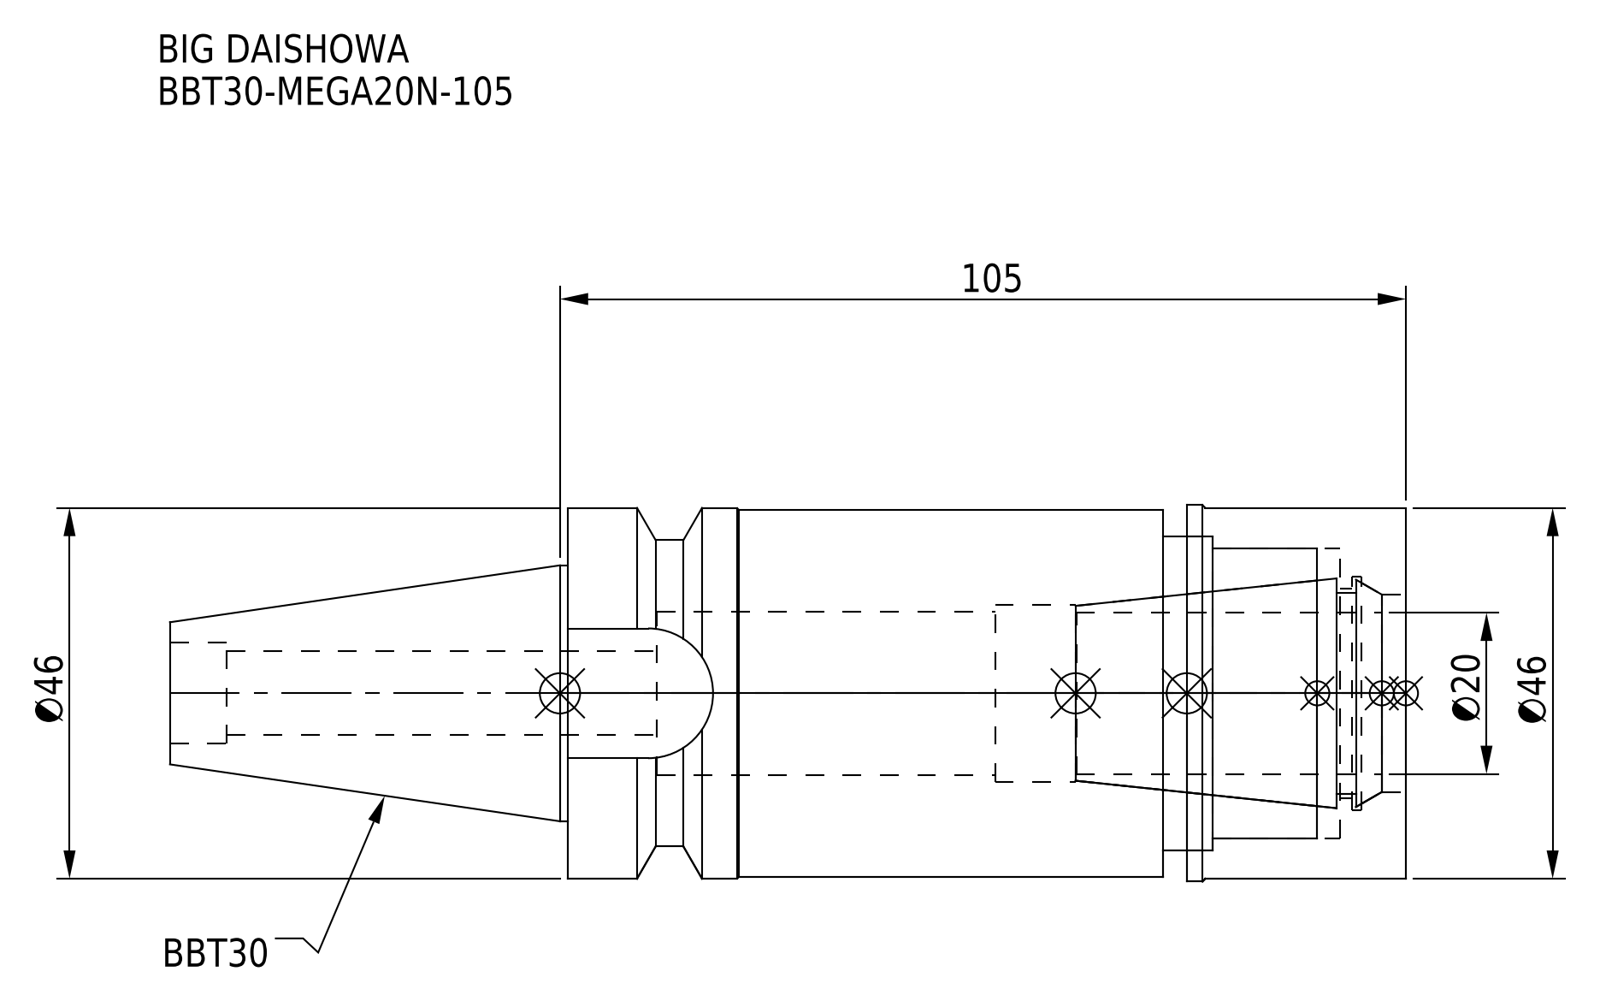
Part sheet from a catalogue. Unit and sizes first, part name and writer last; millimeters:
Units: millimetres
Overall size (bounding box): 153.4 × 46.7 × 46.7
Round holes (diameter × count): ⌀10.4 ×1, ⌀12.5 ×1, ⌀20.3 ×1, ⌀22 ×1, ⌀24.5 ×1, ⌀26 ×1, ⌀29 ×1, ⌀36 ×1, ⌀39 ×1
Round bosses / shafts (diameter × count): ⌀46.7 ×1, ⌀46 ×1, ⌀45.5 ×1, ⌀31.75 ×1
Partial cylindrical surfaces — rounded edges, fillets, slot ends (radius × count): R8.05 ×1, R19 ×1
Main face-to-face distances: 104, 11, 93, 27.2, 76.8, 8.2, 19, 95.8, 30.2, 22
Volume: 143 989 mm³ · Surface area: 36 746 mm²
Bodies: 2 solids, 76 faces (22 planar, 40 cylindrical, 14 other)
Part name (STEP PRODUCT): BBT30-MEGA20N-105-200.stp; MGN20_1.stp; BBT30-MEGA20N-105_1.stp; DXF_TEMP_ASSY_ASM_4_ASM.stp (+3 more)
STEP written by: SolidWorks 2019 (CONFIG_CONTROL_DESIGN)
